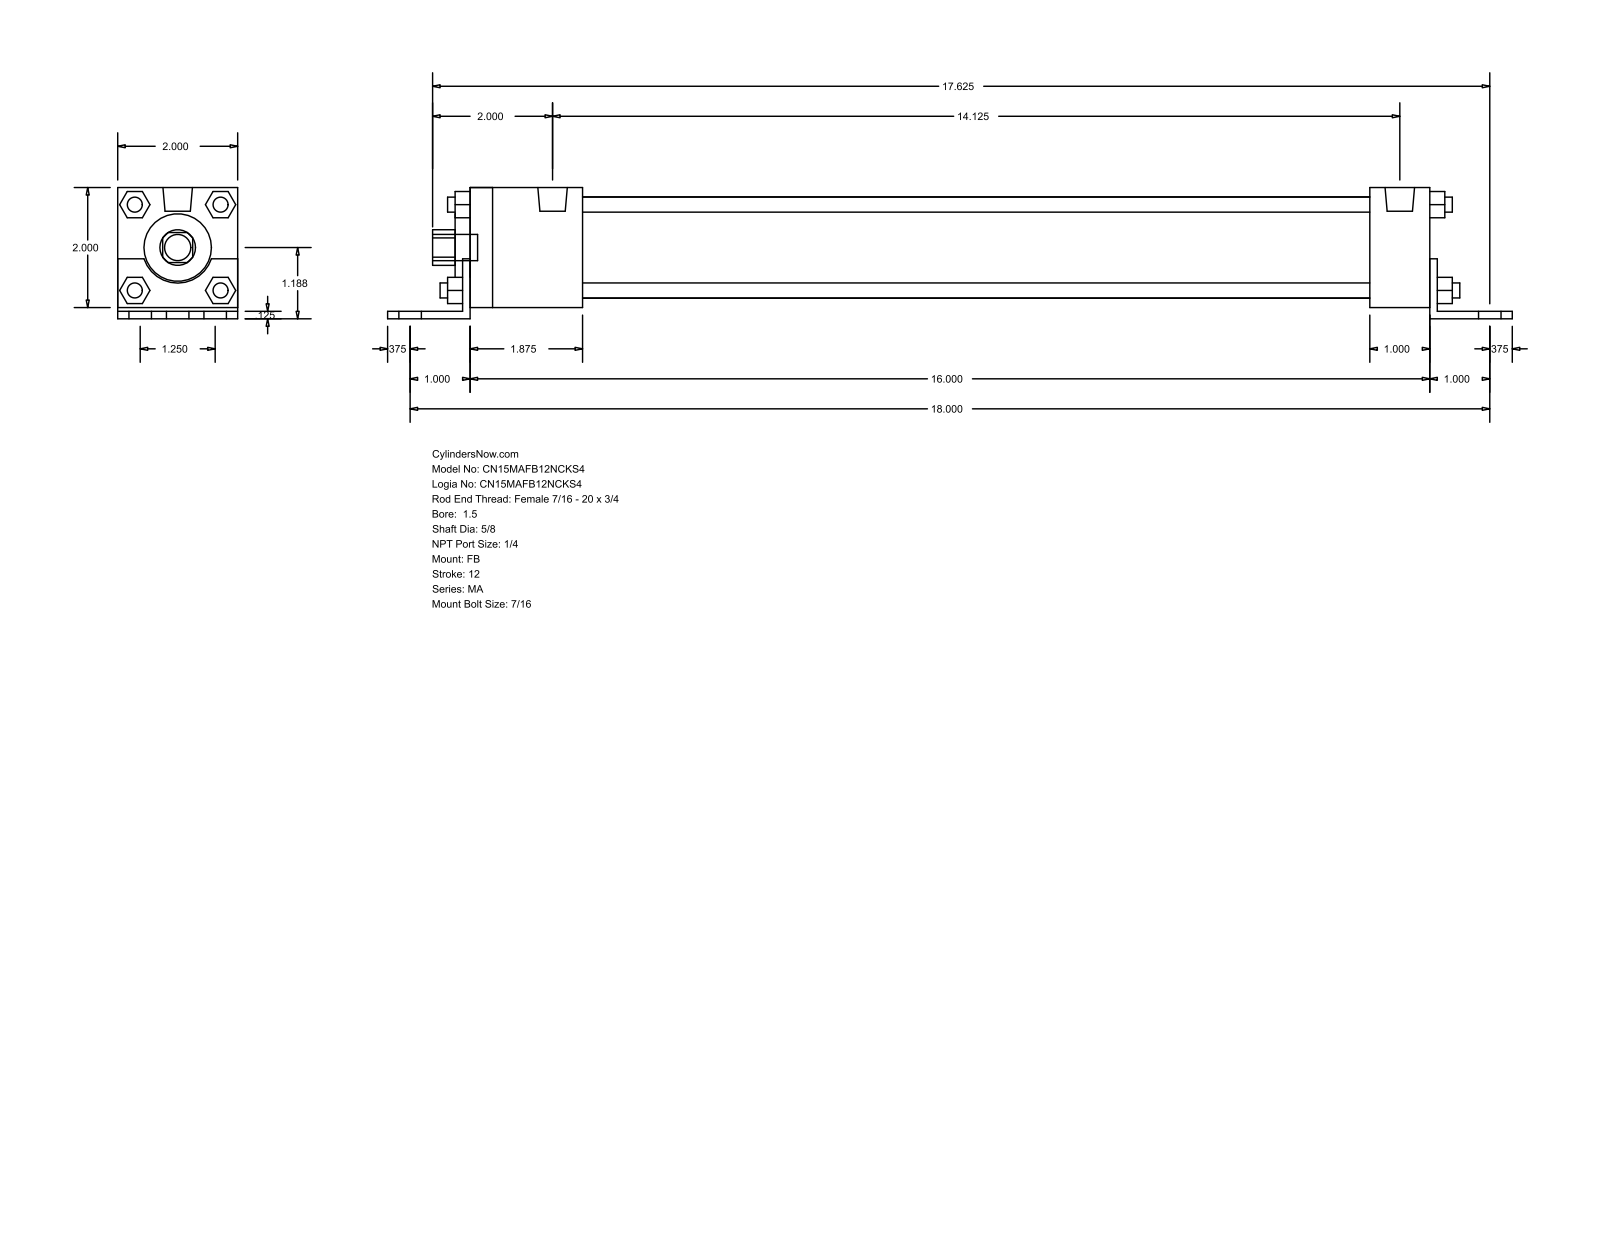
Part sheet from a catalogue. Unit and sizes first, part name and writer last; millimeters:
Units: millimetres
Overall size (bounding box): 476.25 × 55.56 × 50.8
Round holes (diameter × count): ⌀15.88 ×1, ⌀28.57 ×1, ⌀42.93 ×1
Round bosses / shafts (diameter × count): ⌀11.11 ×7, ⌀7.94 ×4, ⌀6.35 ×4, ⌀12.49 ×2
Partial cylindrical surfaces — rounded edges, fillets, slot ends (radius × count): R7.54 ×1, R15.05 ×1
Main face-to-face distances: 50.8, 3.17, 4.76, 55.56, 1.59, 52.39, 3.18, 409.57, 6.35, 415.92
Bodies: 0 solids, 140 faces (105 planar, 35 cylindrical, 0 other)
Part name (STEP PRODUCT): MA_FB__0150_0.625
STEP written by: GSSL Pune (CONFIG_CONTROL_DESIGN)
